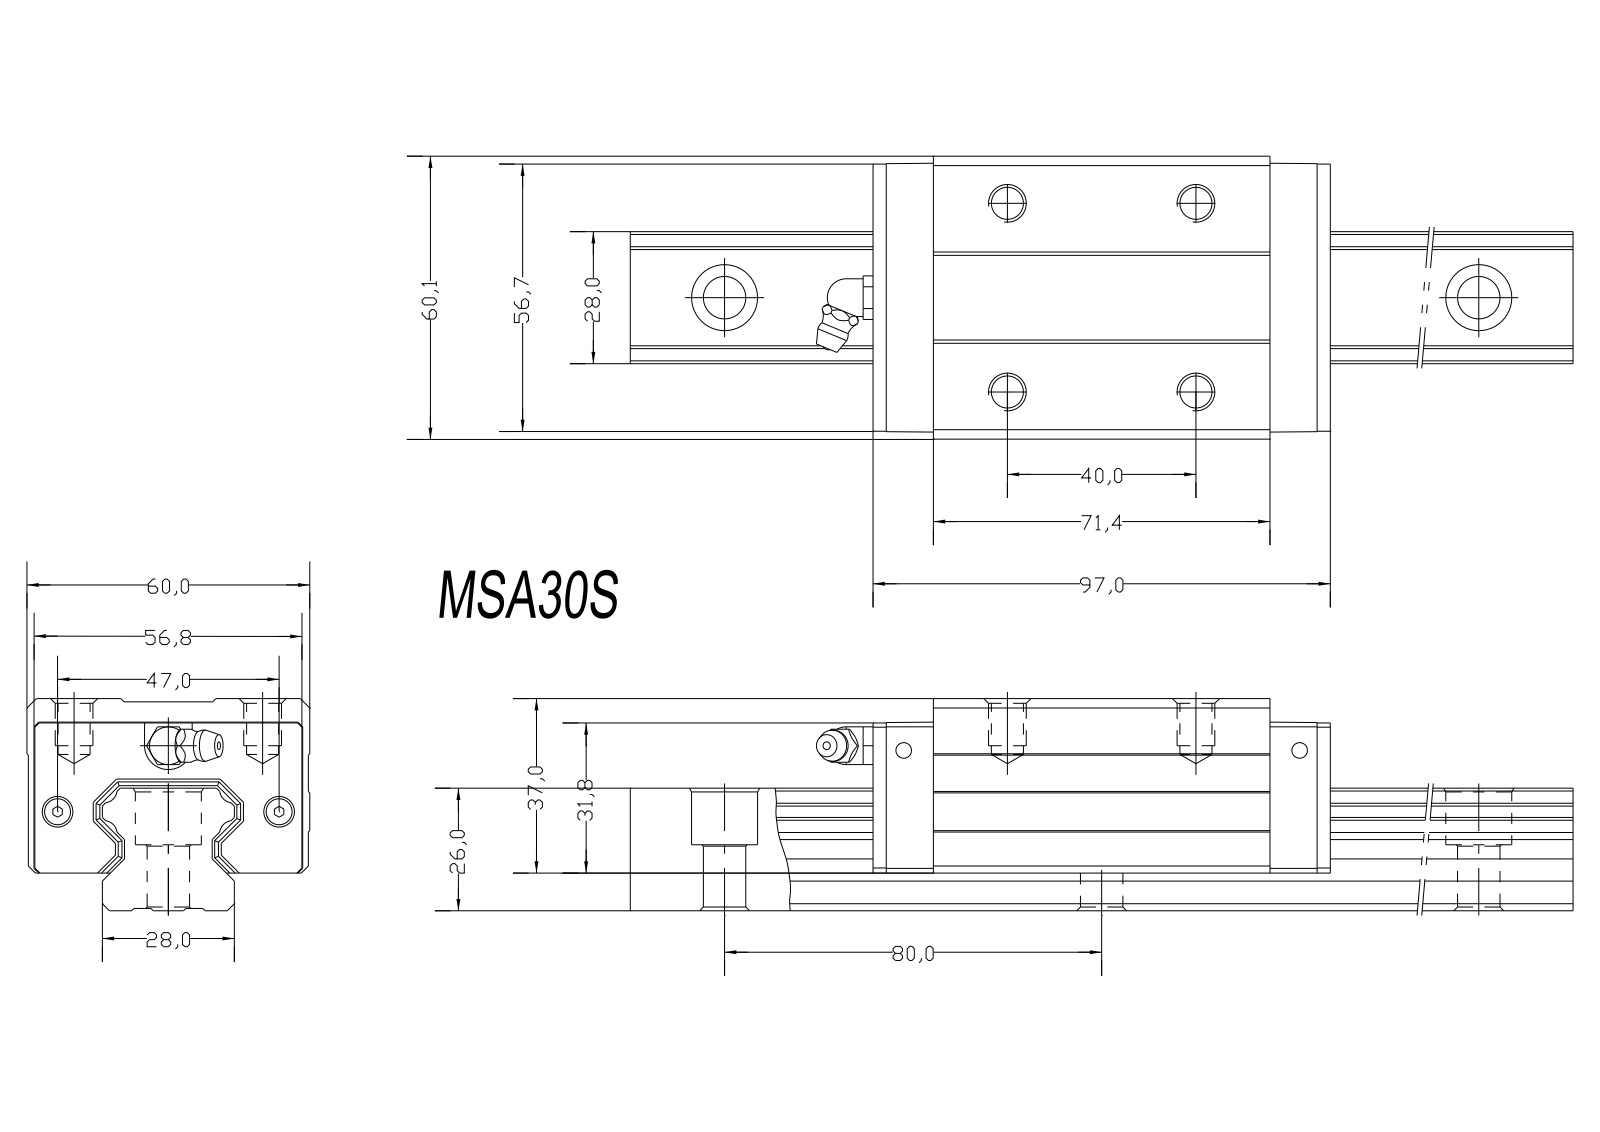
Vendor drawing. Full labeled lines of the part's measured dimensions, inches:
STEP written by: Kubotek KeyCreator V6.5.2 (0407) (CONFIG_CONTROL_DESIGN)
Units: inches
Bodies: 3 solids, 213 faces (140 planar, 56 cylindrical, 17 other)
Overall size (bounding box): 11.024 × 2.362 × 1.772
Volume: 19.63 in³ · Surface area: 98.98 in²
Round holes (diameter × count): ⌀0.315 ×4, ⌀0.354 ×4, ⌀0.551 ×4, ⌀0.256 ×3, ⌀0.128 ×2
Round bosses / shafts (diameter × count): ⌀0.315 ×1
Partial cylindrical surfaces — rounded edges, fillets, slot ends (radius × count): R0.122 ×4, R0.199 ×1
Main face-to-face distances: 1.024, 0.315, 0.709, 0.188, 0.915, 0.806, 1.533, 0.618, 1.72, 1.772
Hole centre spacings: 1.113, 1.575, 2.49, 4.015, 5.568, 3.15, 1.077, 2.227
